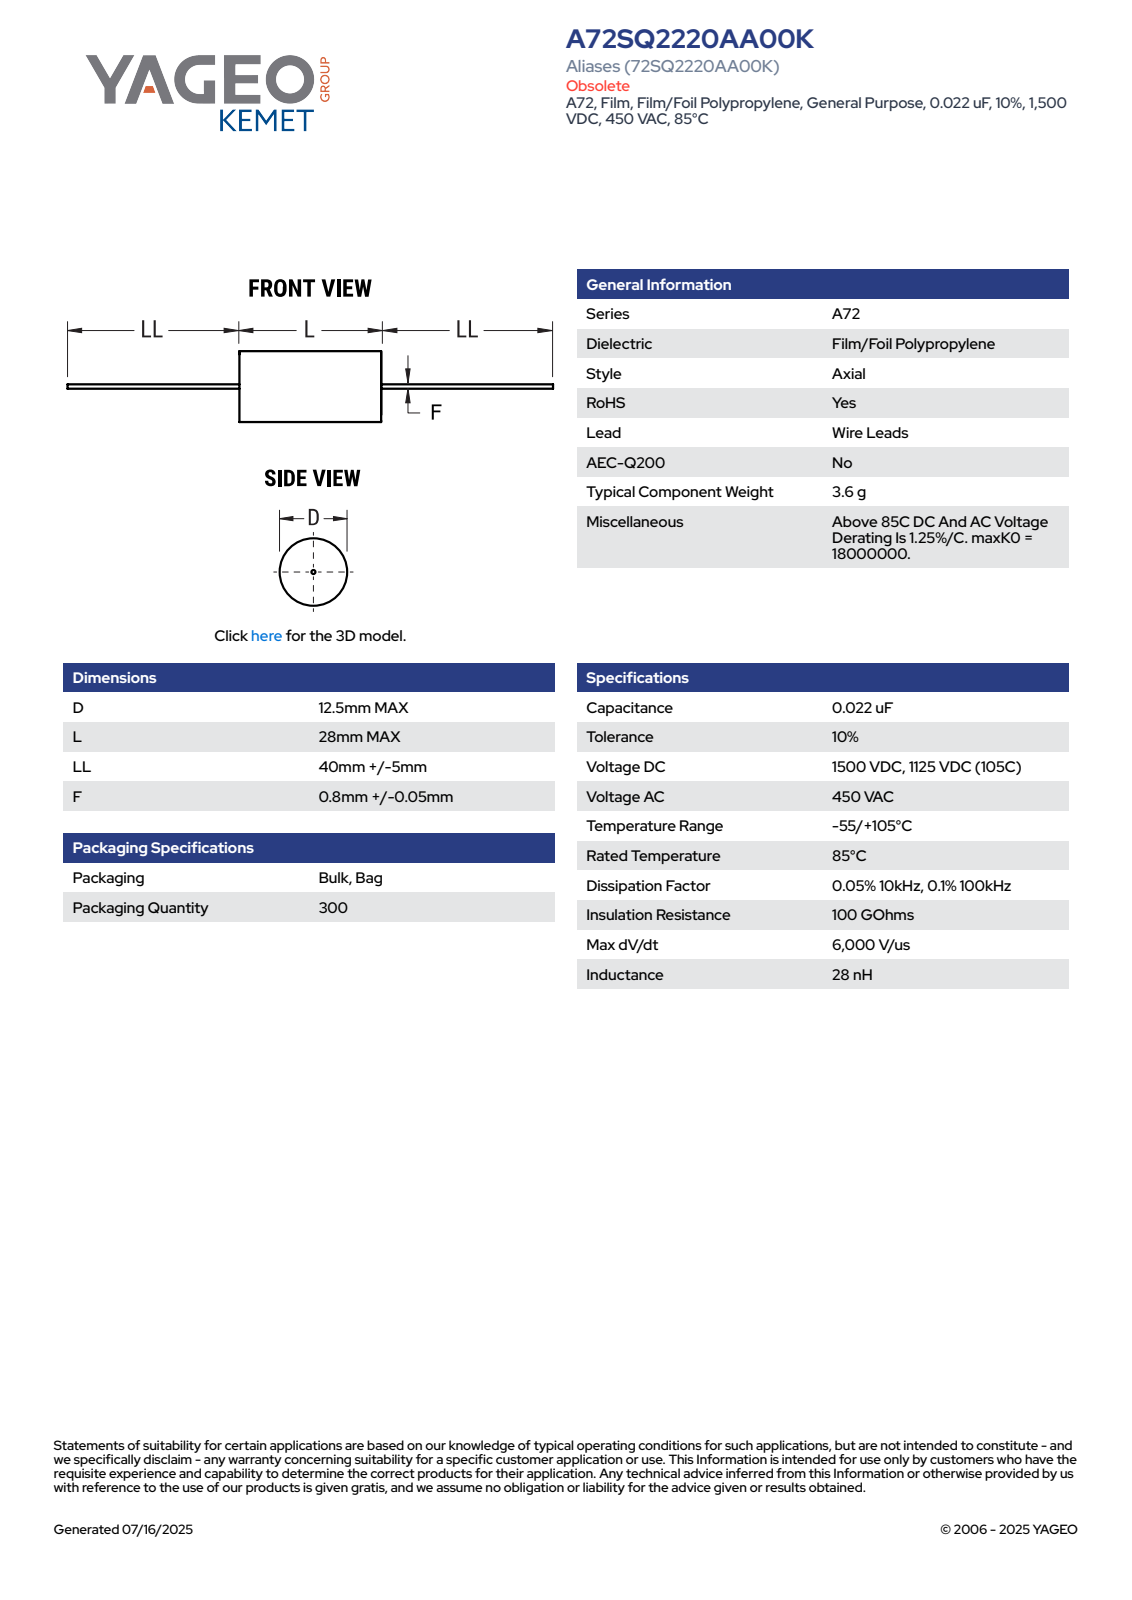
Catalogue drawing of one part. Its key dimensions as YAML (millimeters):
part_name: "CFA_ACWF_12.5X28_D12.5L28LL45F0.85"
step_written_by: "SolidWorks 2014 (AUTOMOTIVE_DESIGN)"
units: millimeters
bodies: {solids: 1, faces: 72, planar: 26, cylindrical: 15, other: 31}
overall_size: [118, 12.51, 12.5]
volume: 3487
surface_area: 1586
round_bosses_or_shafts:
  - {diameter: 12.5, count: 1}
  - {diameter: 0.85, count: 1}
partial_cylinders:
  - {radius: 6.26, count: 1}
face_to_face_distances: [28, 45, 73, 118]
